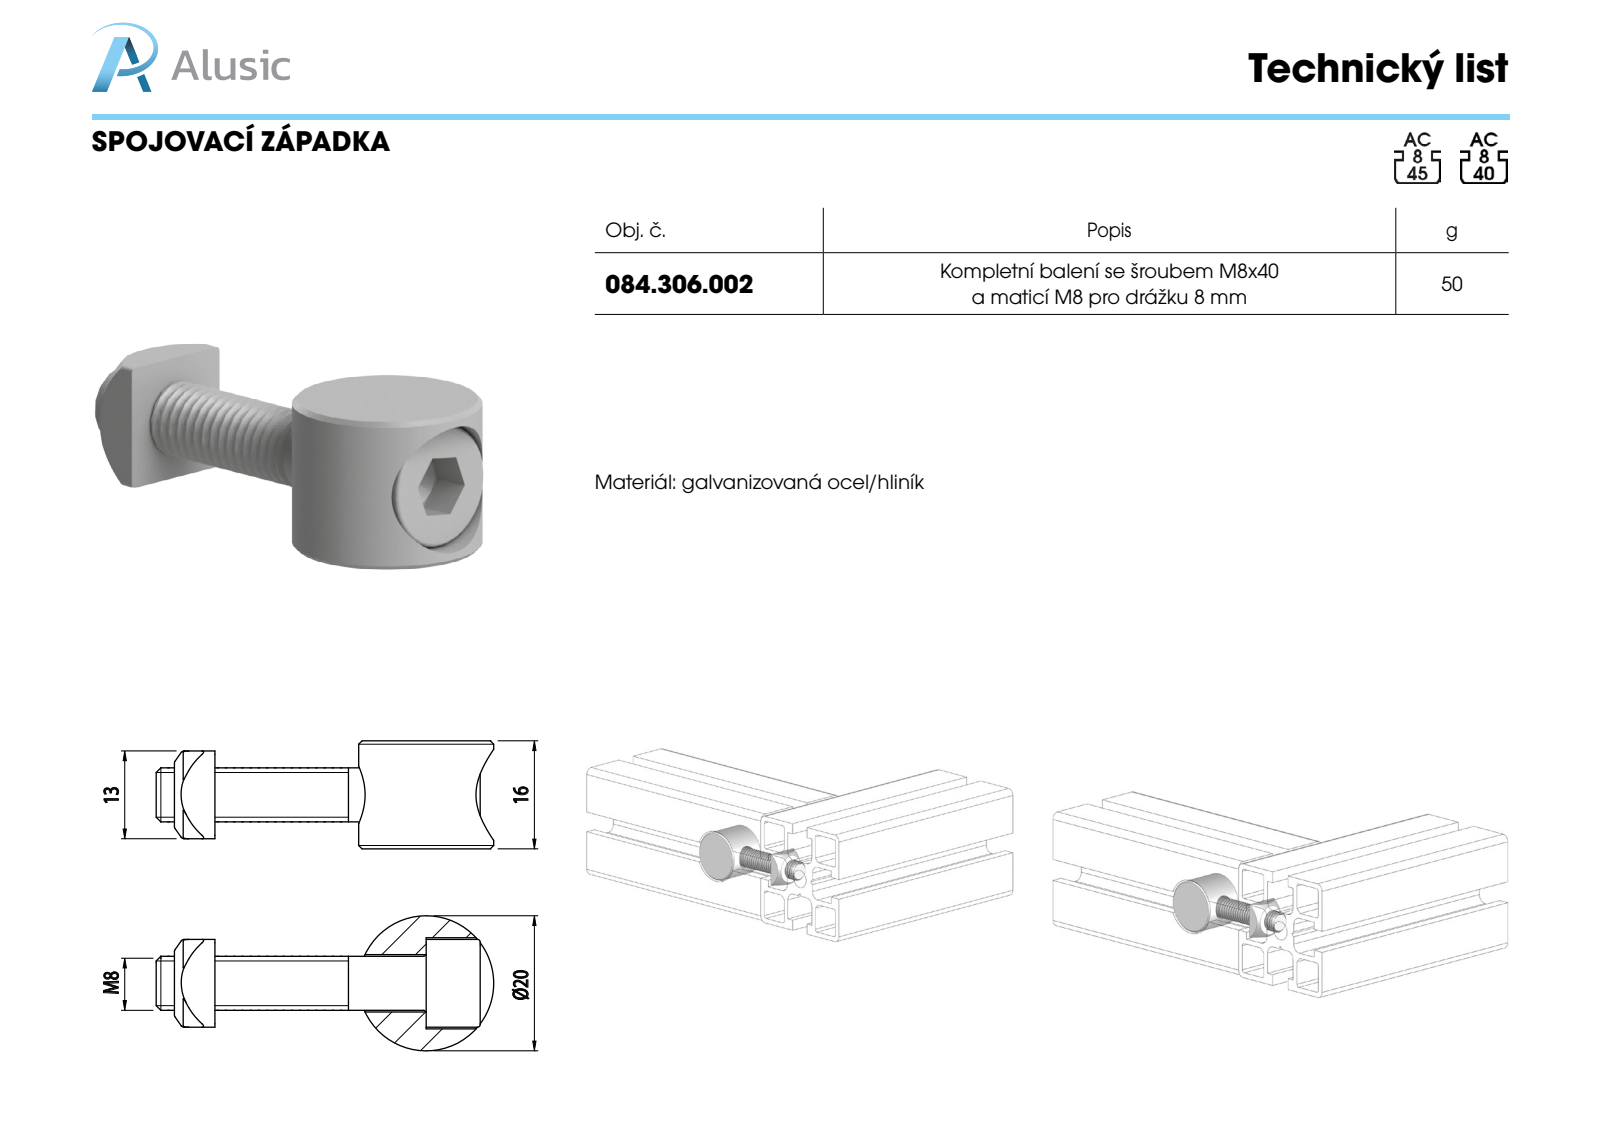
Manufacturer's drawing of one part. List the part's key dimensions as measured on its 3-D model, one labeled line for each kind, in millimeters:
Part name (STEP PRODUCT): 084.306.002
STEP written by: SolidWorks 2011 (CONFIG_CONTROL_DESIGN)
Units: millimetres
Bodies: 1 solid, 13 faces (3 planar, 6 cylindrical, 4 other)
Overall size (bounding box): 20 × 20 × 16
Volume: 3 112 mm³ · Surface area: 2 096 mm²
Round holes (diameter × count): ⌀8.5 ×1, ⌀13.5 ×1
Round bosses / shafts (diameter × count): ⌀20 ×1
Main face-to-face distances: 16
